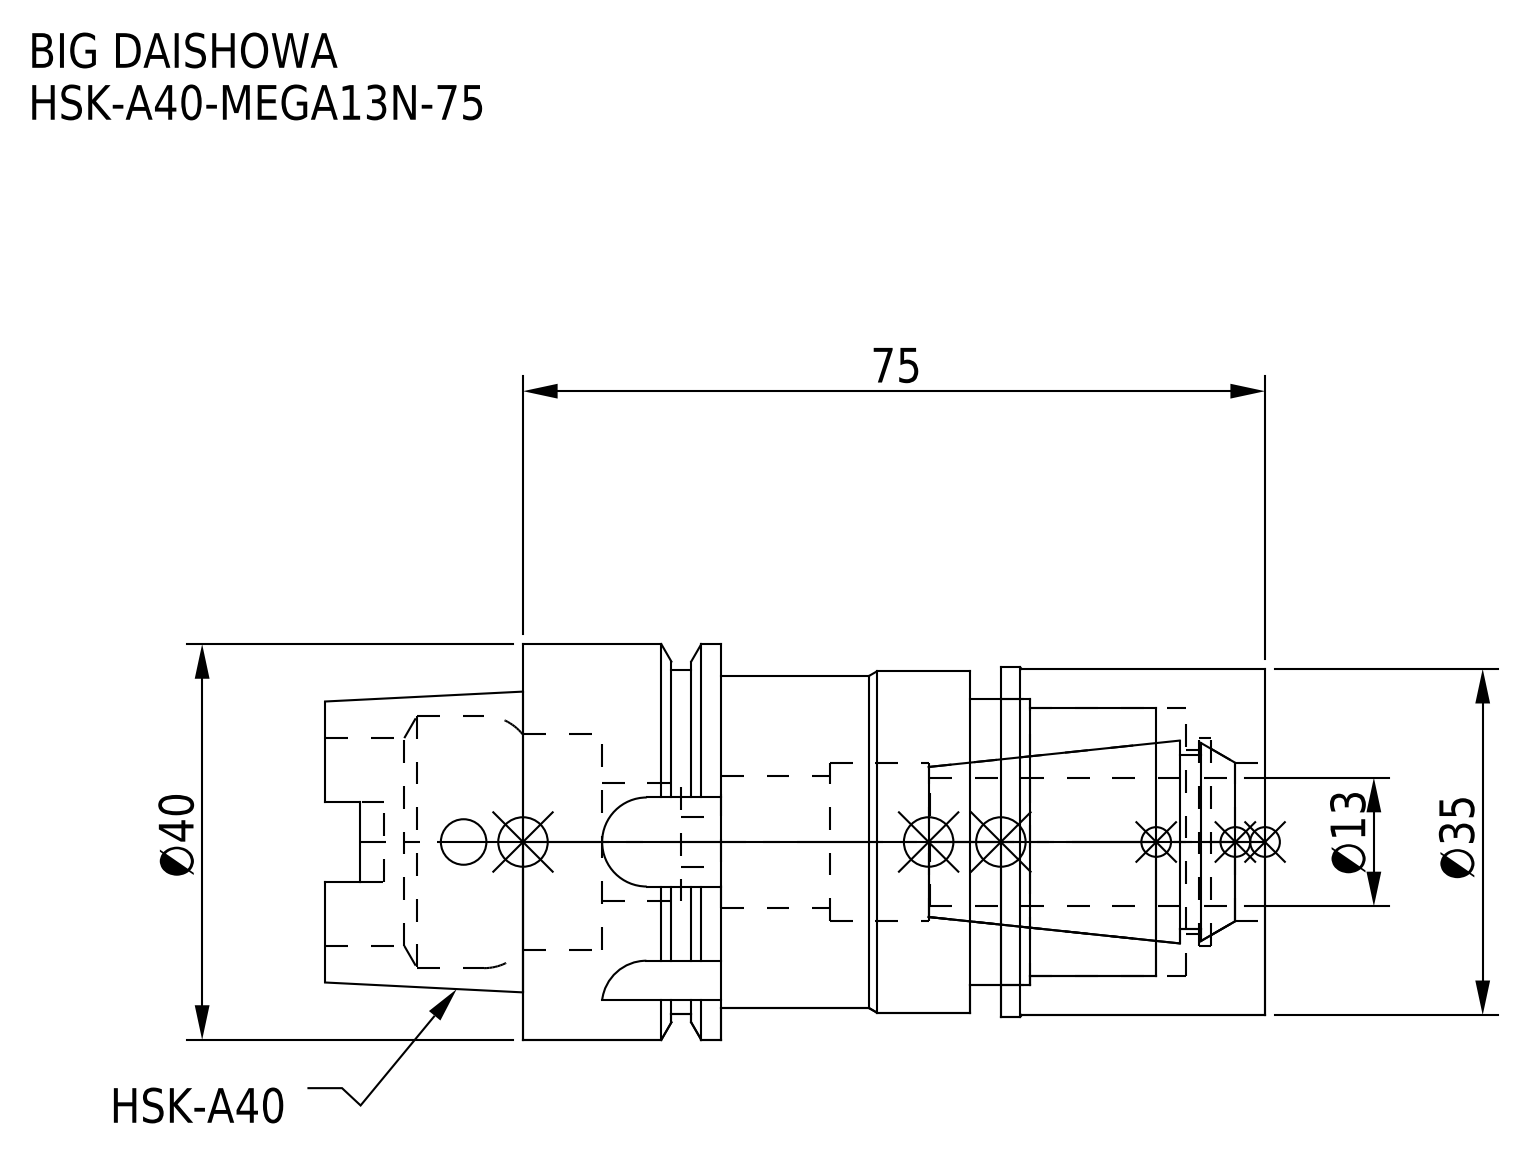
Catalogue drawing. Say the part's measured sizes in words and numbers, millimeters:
The part is named "HSK-A40-MEGA13N-75; HSK-A40-MEGA13N-75-130.stp; HSK-A40-MEGA13N-75-130-FreeParts; DXF_TEMP_ASSY_ASM_4_ASM.stp (+3 more)". Its 3-D file was written by "SolidWorks 2019 (CONFIG_CONTROL_DESIGN)". It is 2 solids with 127 faces: 47 planar, 58 cylindrical and 22 other. Overall it measures 95 by 40 by 40 millimeters. Its volume is 62 102 cubic millimeters and its surface area 22 692 square millimeters. Round holes: 1 of diameter 4.6, 1 of diameter 5, 1 of diameter 12, 1 of diameter 13.3, 1 of diameter 16, 1 of diameter 18.5, 1 of diameter 21, 1 of diameter 21.8, 1 of diameter 25.5, 1 of diameter 27, 1 of diameter 29. Round bosses or shafts: 1 of diameter 40, 1 of diameter 35.3, 1 of diameter 35, 1 of diameter 34.8, 1 of diameter 34.5, 1 of diameter 33.6. Partial cylindrical surfaces (rounded edges, fillets, slot ends): 4 of radius 1.88, 4 of radius 4.5. The main face-to-face distances are 20, 75, 55, 8, 48.3, 47, 59.05, 3, 11, 44.
